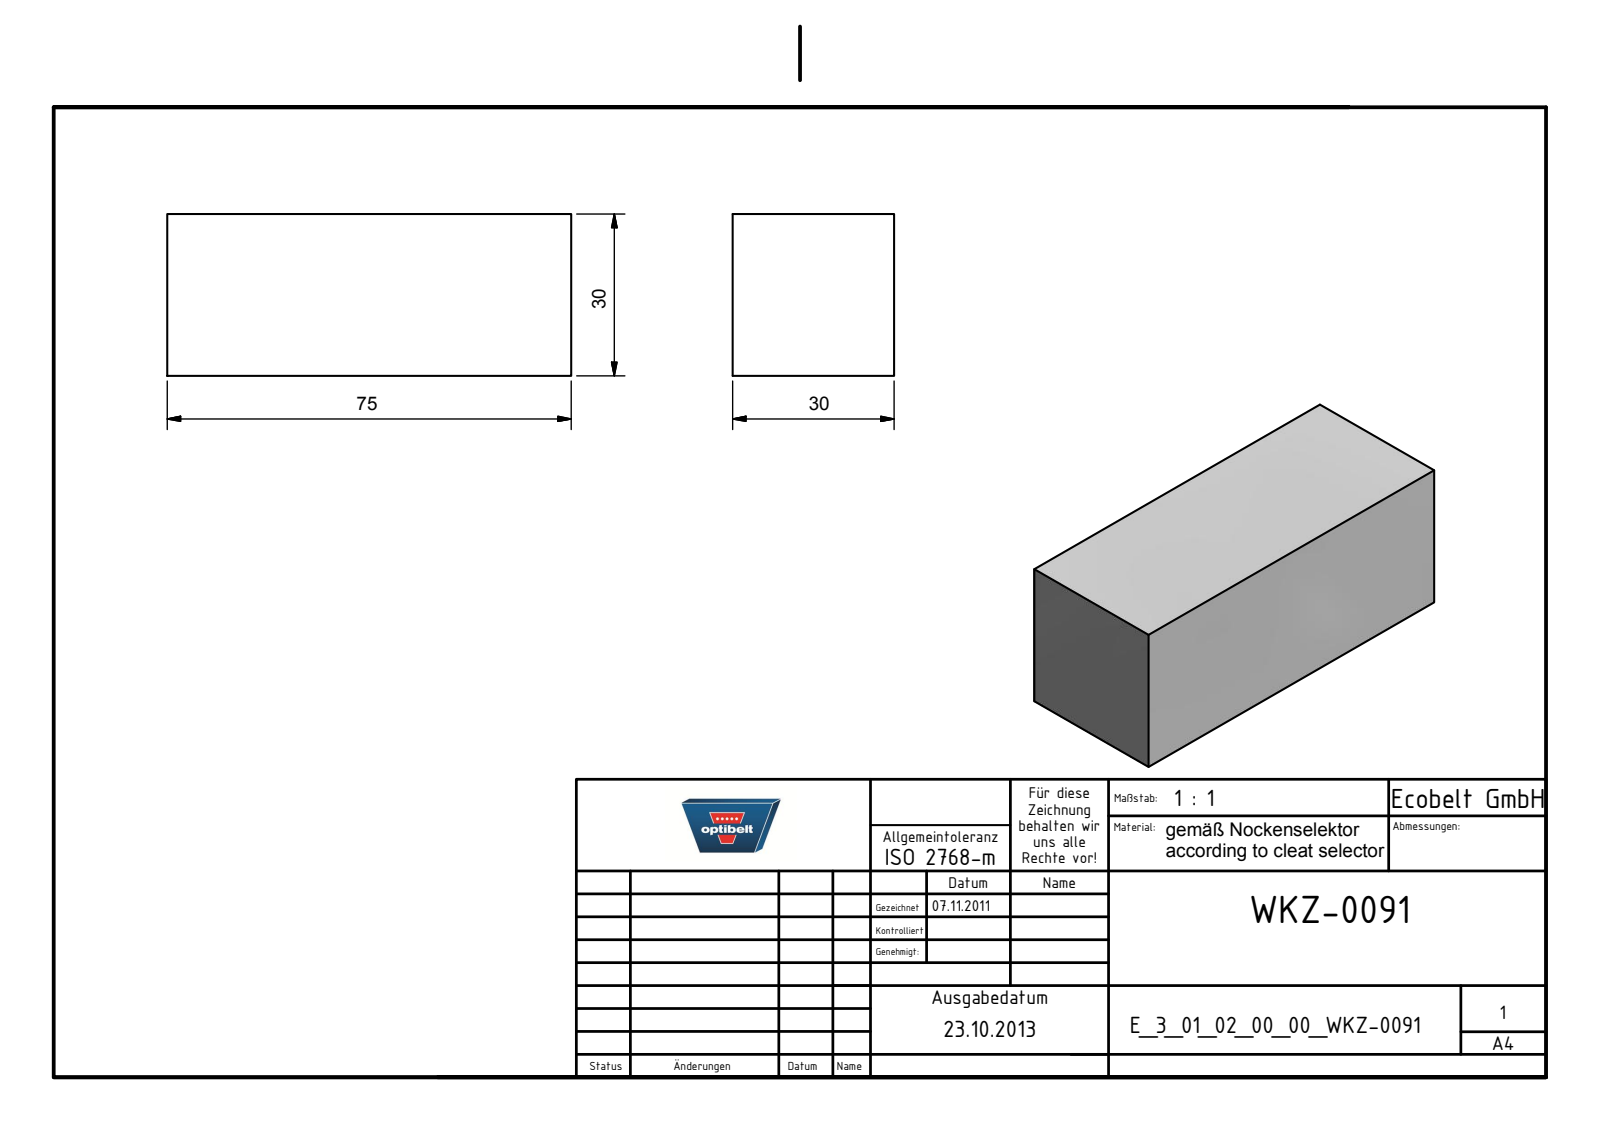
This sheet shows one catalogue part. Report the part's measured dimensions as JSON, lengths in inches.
{"part_name": "E_3_01_02_00_00_WKZ-0091", "step_written_by": "Autodesk Inventor 2021 (AUTOMOTIVE_DESIGN)", "units": "inches", "bodies": {"solids": 1, "faces": 6, "planar": 6, "cylindrical": 0, "other": 0}, "overall_size": [2.953, 1.181, 1.181], "volume_in3": 4.119, "surface_area_in2": 16.74, "face_to_face_distances": [1.181, 2.953]}
